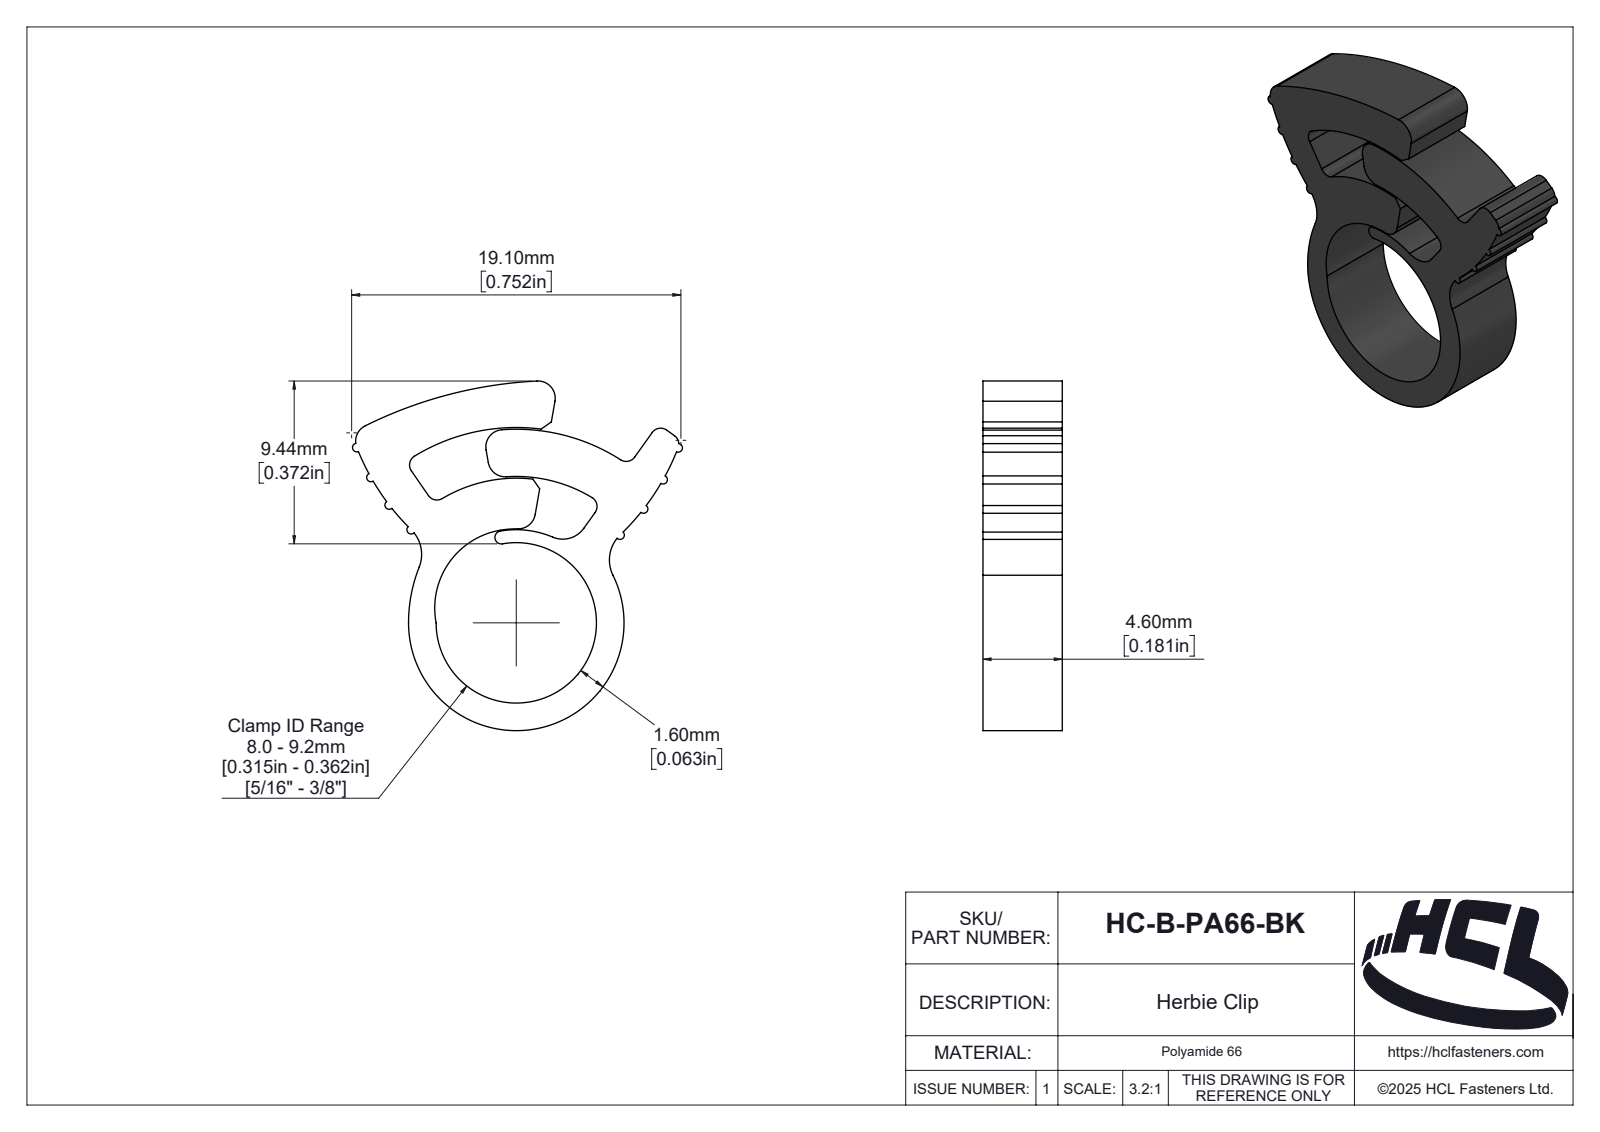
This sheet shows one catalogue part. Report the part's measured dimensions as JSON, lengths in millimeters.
{"part_name": "HC-B-PA66-BK", "step_written_by": "SolidWorks 2025 (AUTOMOTIVE_DESIGN)", "units": "millimeters", "bodies": {"solids": 1, "faces": 162, "planar": 13, "cylindrical": 100, "other": 49}, "overall_size": [20.27, 19.14, 4.6], "volume_mm3": 654, "surface_area_mm2": 939, "partial_cylinders_radius": [[0.25, 8], [0.6, 6], [1, 5], [2, 2], [0.17, 1], [0.38, 1], [0.67, 1], [0.84, 1]], "face_to_face_distances": [4.6]}
